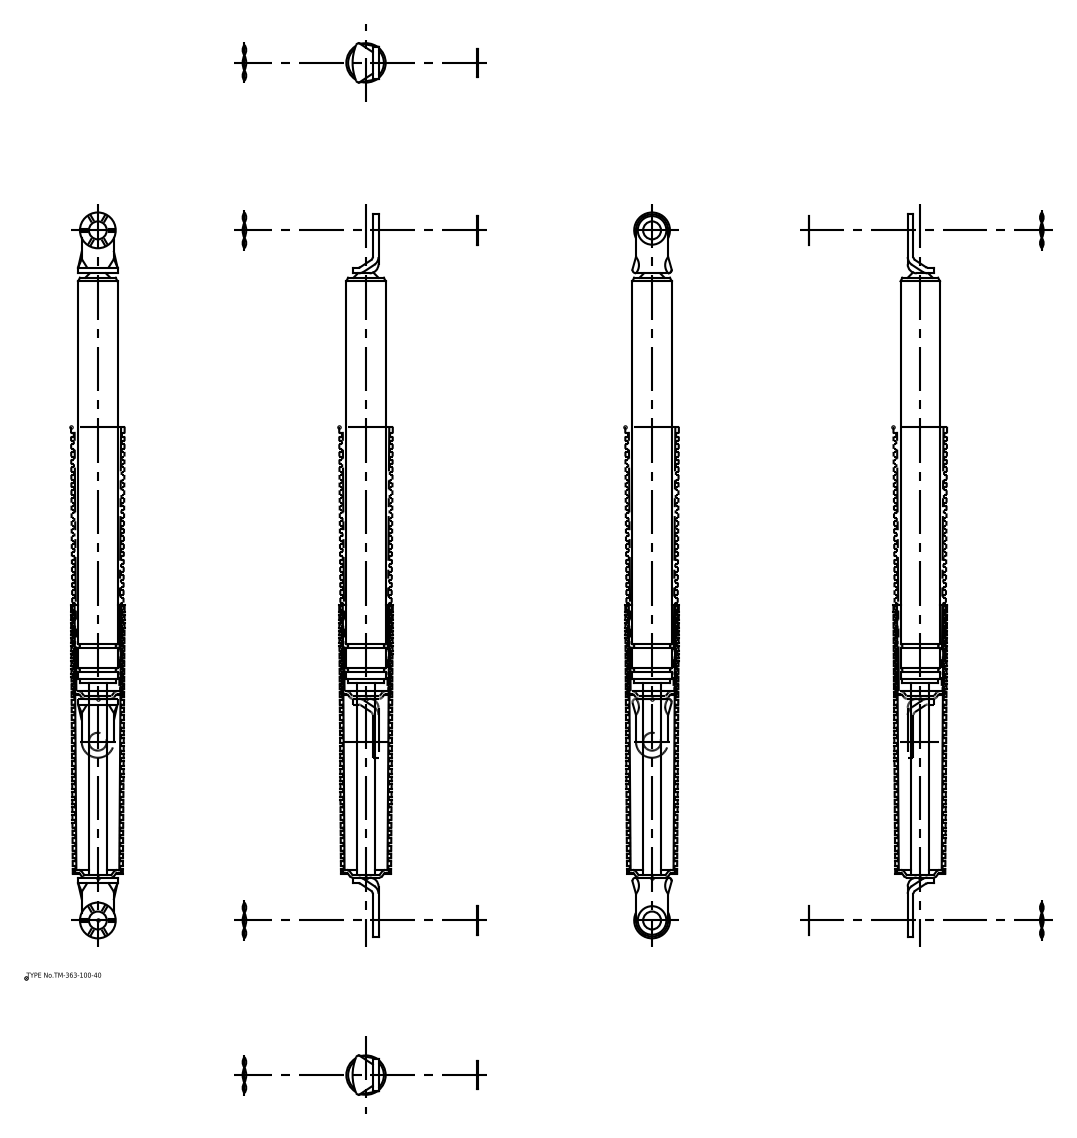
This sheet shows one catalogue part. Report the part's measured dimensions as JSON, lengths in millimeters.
{"part_name": "washer_1; washer_2; cover; body_1", "step_written_by": "spGate 16.7.1 (AUTOMOTIVE_DESIGN)", "units": "millimeters", "bodies": {"solids": 7, "faces": 323, "planar": 115, "cylindrical": 46, "other": 162}, "overall_size": [406, 30, 30], "volume_mm3": 118814, "surface_area_mm2": 60399, "round_holes": [[10, 3]], "round_bosses_or_shafts": [[20, 3], [16, 2], [22.5, 1], [22, 1]], "partial_cylinders_radius": [[3, 2], [4.4, 2], [9, 2], [26.32, 1]], "face_to_face_distances": [4.3, 3.2, 8.6, 12.9, 1.7, 2.6, 6, 6.9, 17.2, 10.3], "hole_center_spacings": [386]}
